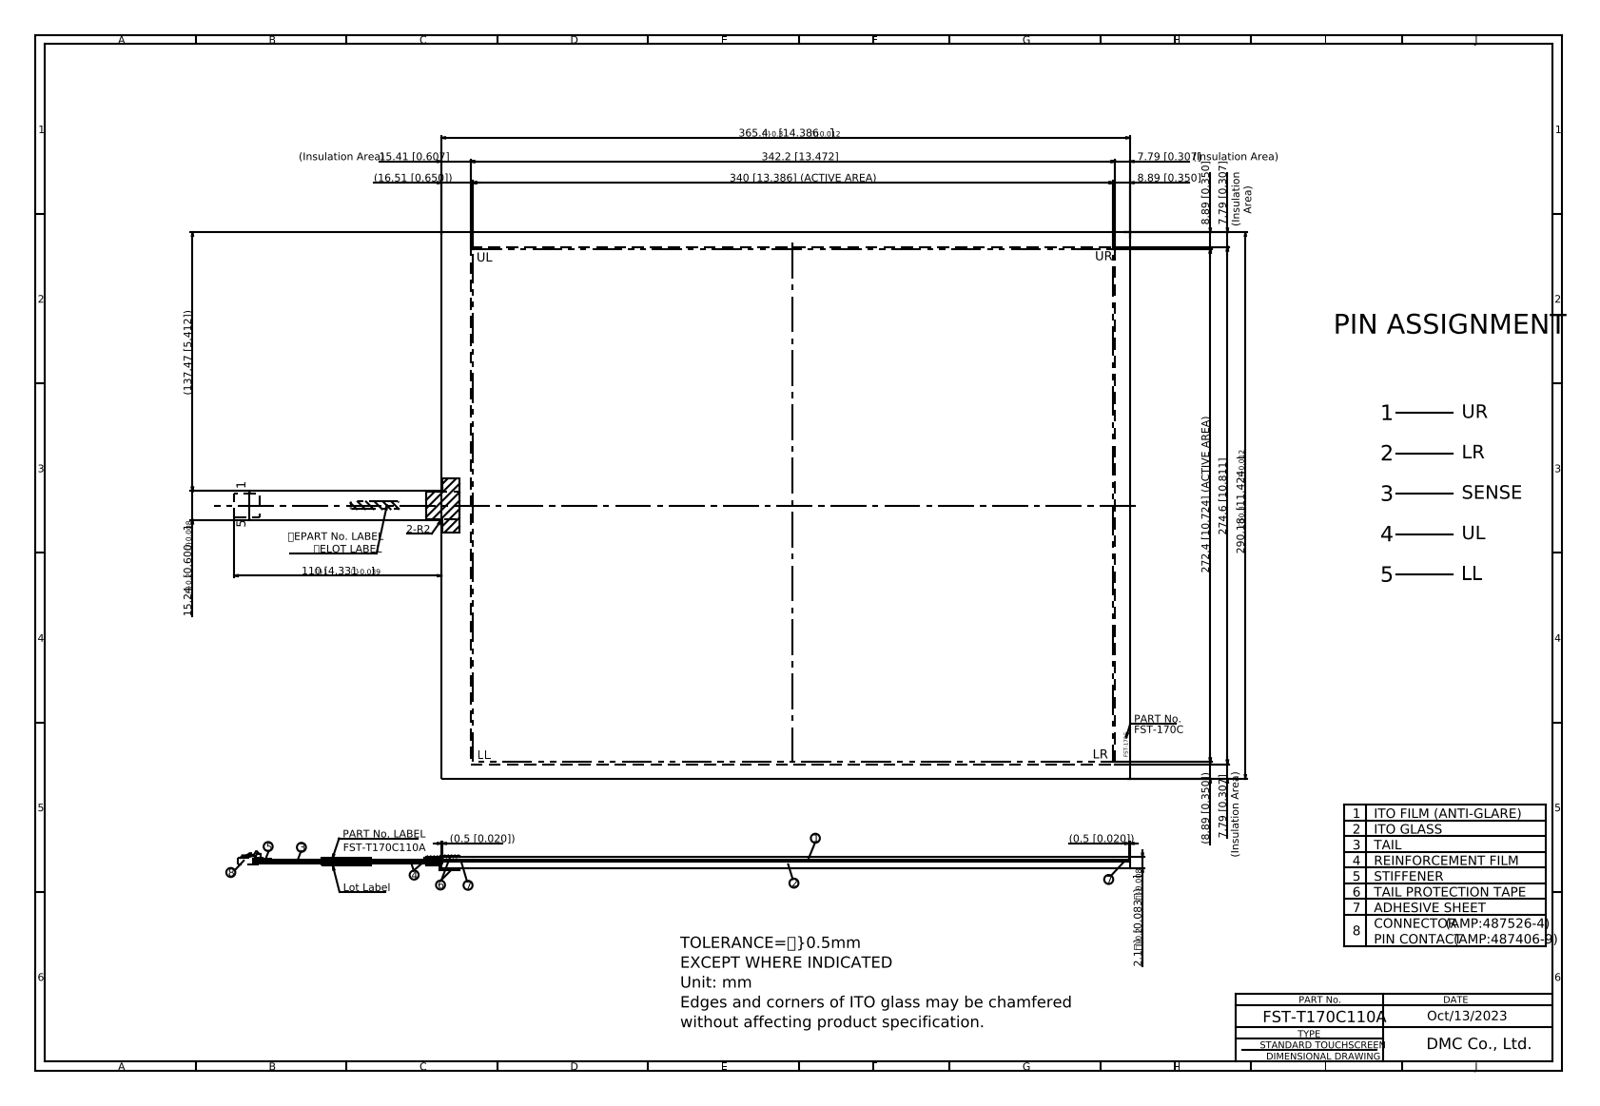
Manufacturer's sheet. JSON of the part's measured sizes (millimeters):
{"part_name": "FST-T170C110A", "step_written_by": "Autodesk Inventor 2020 (AUTOMOTIVE_DESIGN)", "units": "millimeters", "bodies": {"solids": 1, "faces": 43, "planar": 43, "cylindrical": 0, "other": 0}, "overall_size": [548.49, 406.25, 3.15], "volume_mm3": 213835, "surface_area_mm2": 218363, "face_to_face_distances": [2, 2.1, 1.8, 1.9, 290.18, 365.4, 0.65, 0.75, 0.85, 1.15]}
